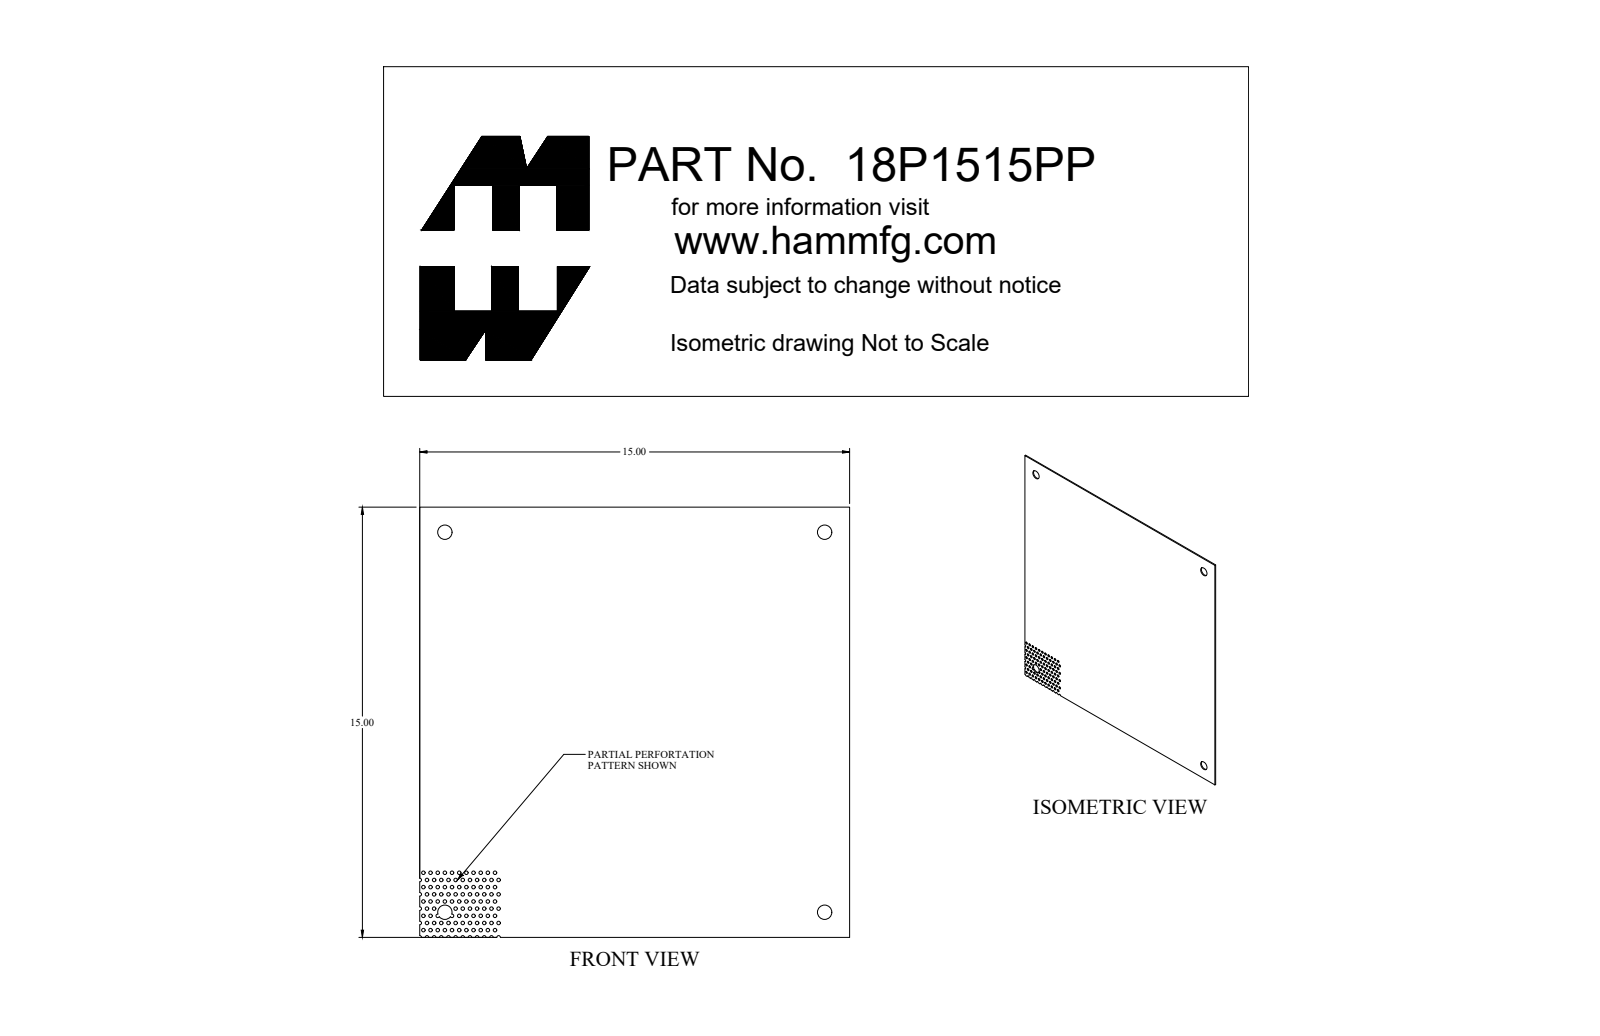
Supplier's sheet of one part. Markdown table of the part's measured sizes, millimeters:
| quantity | value |
| --- | --- |
| part name | 18P1515PP_Default |
| STEP written by | SolidWorks 2018 (CONFIG_CONTROL_DESIGN) |
| units | millimeters |
| bodies | 1 solid, 251 faces (21 planar, 230 cylindrical, 0 other) |
| overall size | 381 × 381 × 1.4 |
| volume | 208 300 mm³ |
| surface area | 291 500 mm² |
| round holes (diameter × count) | 3.2 × 94, 12.7 × 4 |
| partial cylindrical surfaces (radius × count) | 1.6 × 18 |
| main face-to-face distances | 1.4, 381 |
| hole center spacings | 7.1, 6.4, 12.7, 11.4, 17.1, 23.1, 11.5, 19.1 |
